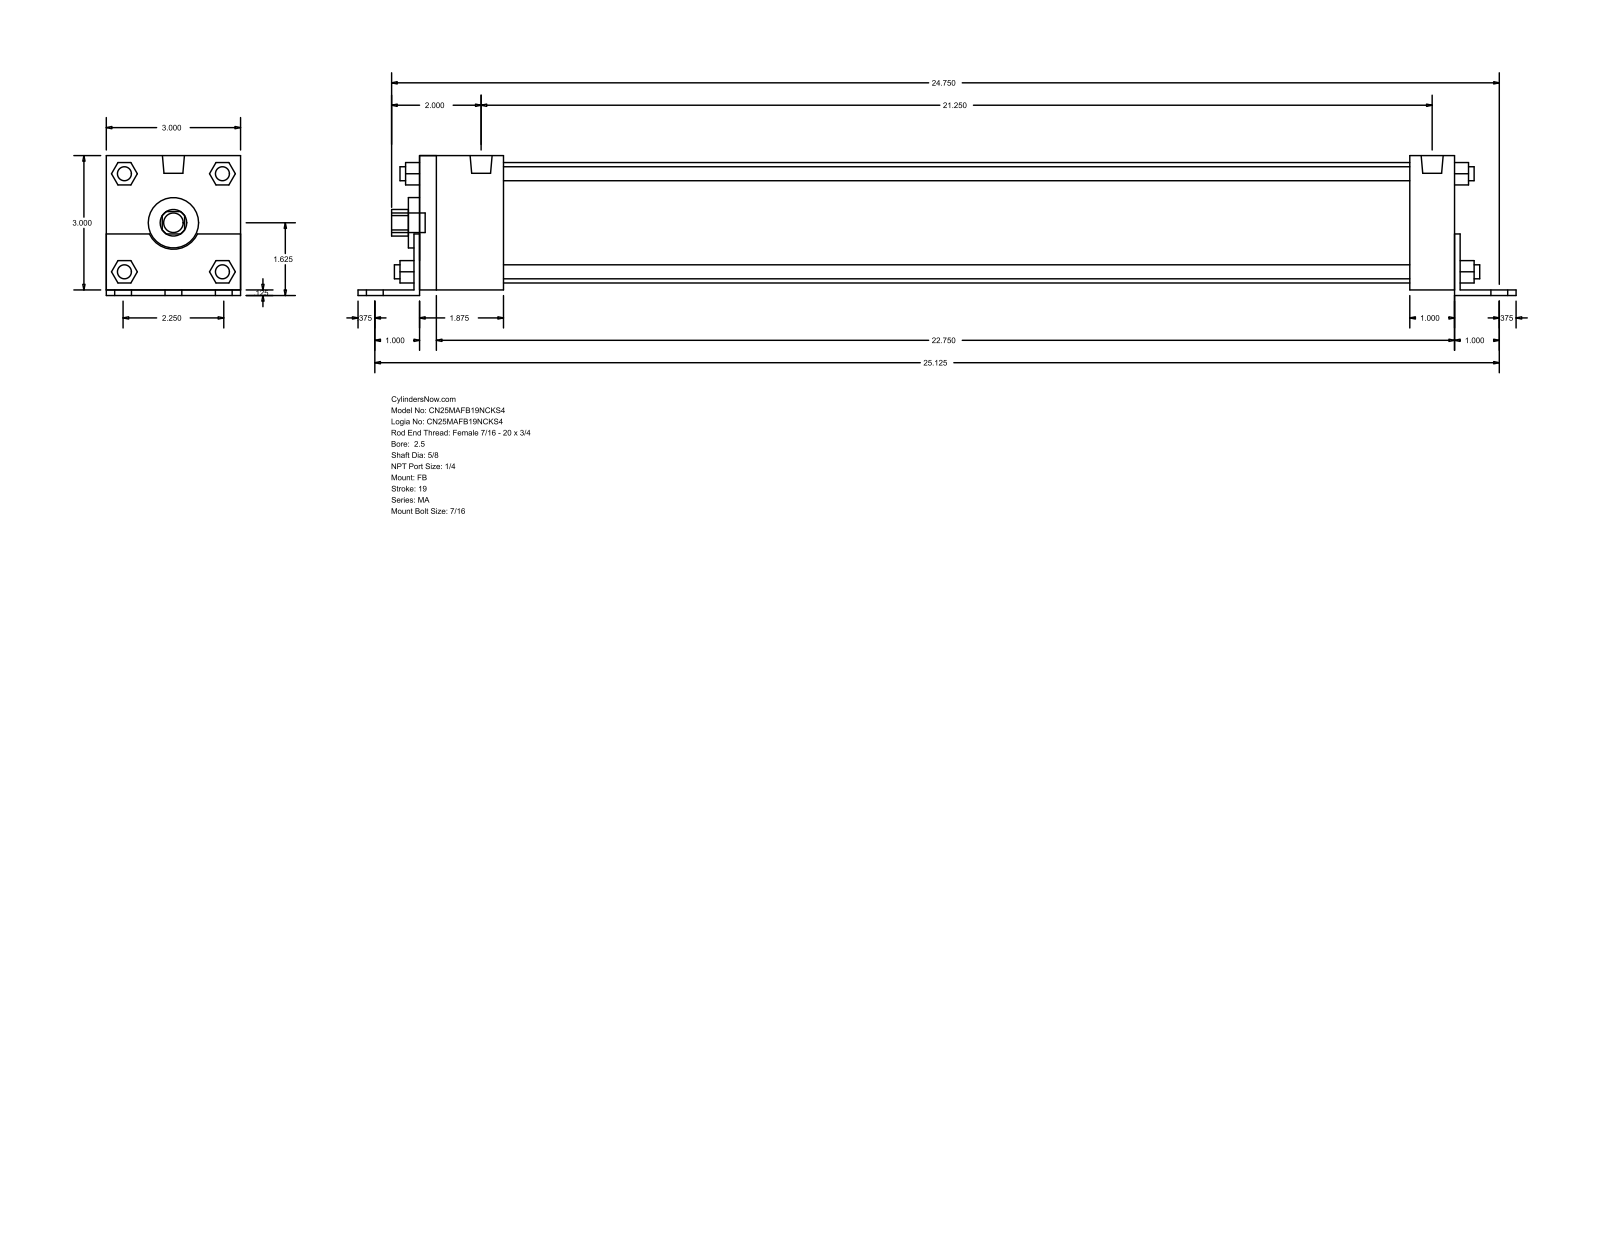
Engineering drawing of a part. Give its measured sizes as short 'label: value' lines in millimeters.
name: MA_FB__0250_0.625
written by: GSSL Pune (CONFIG_CONTROL_DESIGN)
unit: mm
bodies: 0 solids, 140 faces (105 planar, 35 cylindrical, 0 other)
size: 657.23 × 79.38 × 76.2
holes: 1× ⌀15.88, 1× ⌀28.57, 1× ⌀68.33
bosses: 8× ⌀7.94, 7× ⌀11.11, 2× ⌀12.49
rounds: 1× R7.54, 1× R15.05
face distances: 76.2, 3.17, 79.37, 587.37, 593.72, 3.18, 590.54, 47.62, 25.4, 590.55
